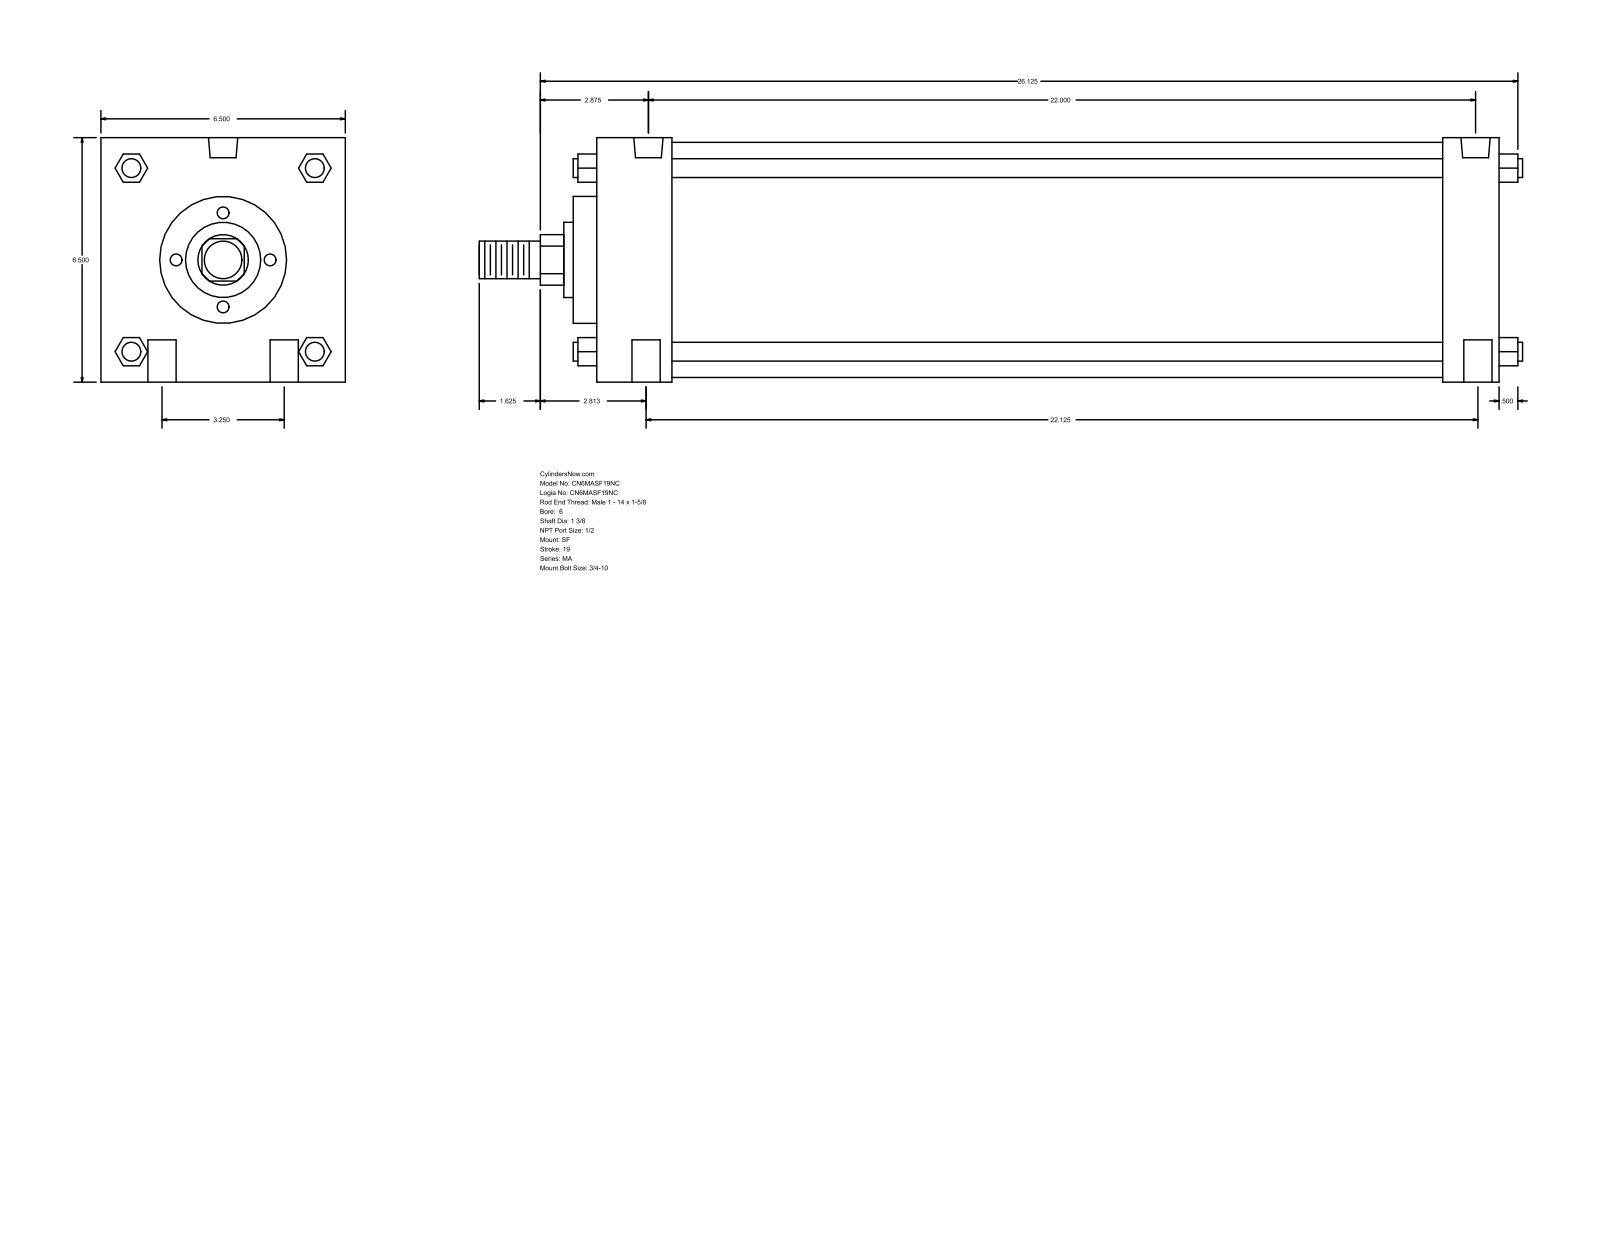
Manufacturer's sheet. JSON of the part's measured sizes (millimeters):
{"part_name": "MA_SF__0600_1.375", "step_written_by": "GSSL Pune (CONFIG_CONTROL_DESIGN)", "units": "millimeters", "bodies": {"solids": 0, "faces": 126, "planar": 95, "cylindrical": 31, "other": 0}, "overall_size": [704.85, 165.1, 165.1], "round_holes": [[19.05, 4], [17.46, 2], [19.77, 2]], "round_bosses_or_shafts": [[12.7, 4], [158.75, 1], [85.72, 1], [50.8, 1], [34.92, 1], [25.4, 1]], "partial_cylinders_radius": [[17.06, 1]], "face_to_face_distances": [165.1, 609.6, 571.5, 50.8, 38.1, 520.7, 558.8, 66.67, 15.87, 587.37], "hole_center_spacings": [41.3, 82.54, 558.8, 561.9, 561.91, 561.97, 568]}
